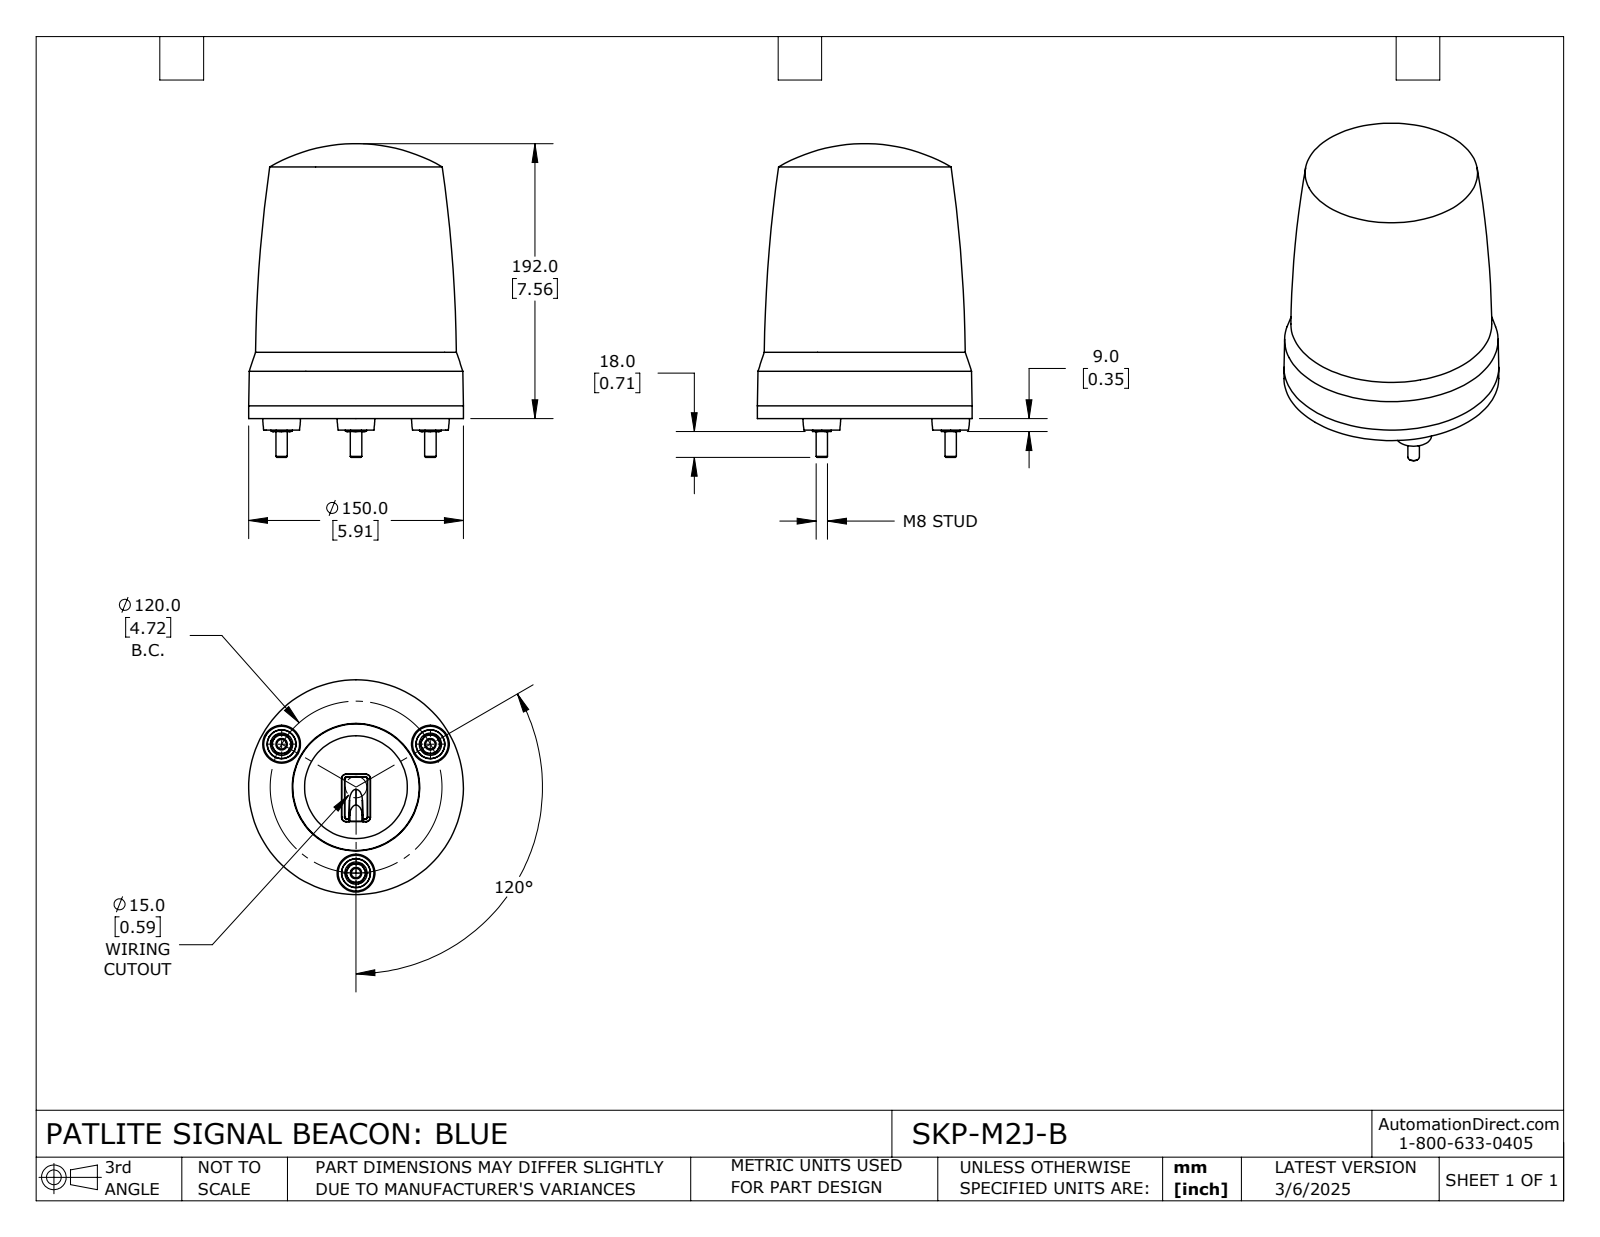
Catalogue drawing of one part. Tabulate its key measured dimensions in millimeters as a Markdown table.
| quantity | value |
| --- | --- |
| part name | SKP-M2J-B |
| STEP written by | SolidWorks 2024 (CONFIG_CONTROL_DESIGN) |
| units | millimeters |
| bodies | 1 solid, 144 faces (49 planar, 14 cylindrical, 81 other) |
| overall size | 219 × 150 × 150 |
| volume | 2 538 000 mm³ |
| surface area | 119 026 mm² |
| round bosses / shafts (diameter × count) | 15.5 × 3, 8 × 3, 150 × 1 |
| main face-to-face distances | 32.7, 8, 40.7, 13, 7.1, 0.9, 33.6, 1.6, 36.05, 41.55 |
